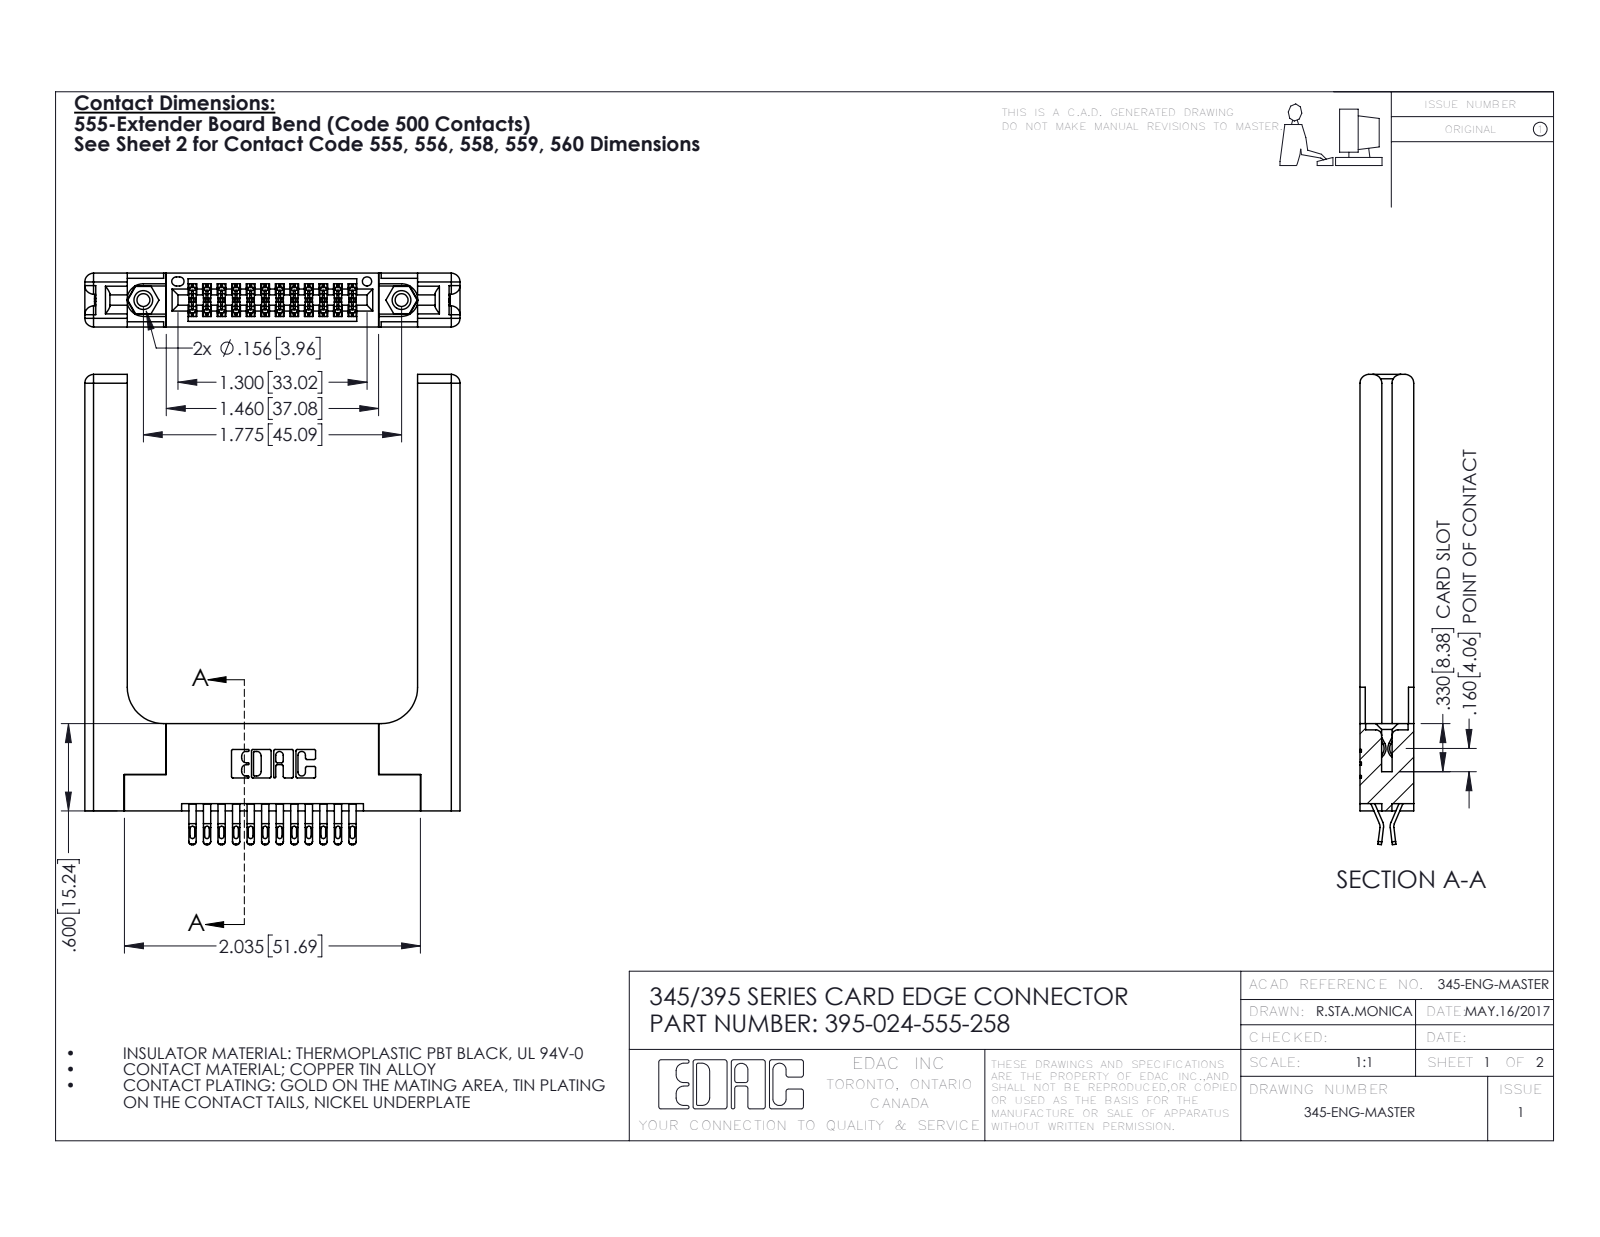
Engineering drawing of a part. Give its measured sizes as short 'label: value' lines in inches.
name: 345-250-001_345-250-001-102; 395-024-555-258; 345-220-058_345-220-058; 345-292-001_555 Tail (+1 more)
written by: SolidWorks 2016 (CONFIG_CONTROL_DESIGN)
unit: in
bodies: 29 solids, 1726 faces (972 planar, 694 cylindrical, 60 other)
size: 3.232 × 2.579 × 0.37
volume: 0.893 in³; area: 21.42 in²
holes: 2× ⌀0.089, 2× ⌀0.125, 2× ⌀0.156, 1× ⌀0.064
bosses: 2× ⌀0.155
rounds: 60× R0.016, 48× R0.02, 36× R0.006, 22× R0.01, 16× R0.06, 6× R0.007, 6× R0.031, 3× R0.026
face distances: 0.37, 0.072, 0.077, 0.148, 0.15, 0.298, 0.22, 0.2, 0.225, 0.025
hole spacings: 0.27, 1.543, 1.775
